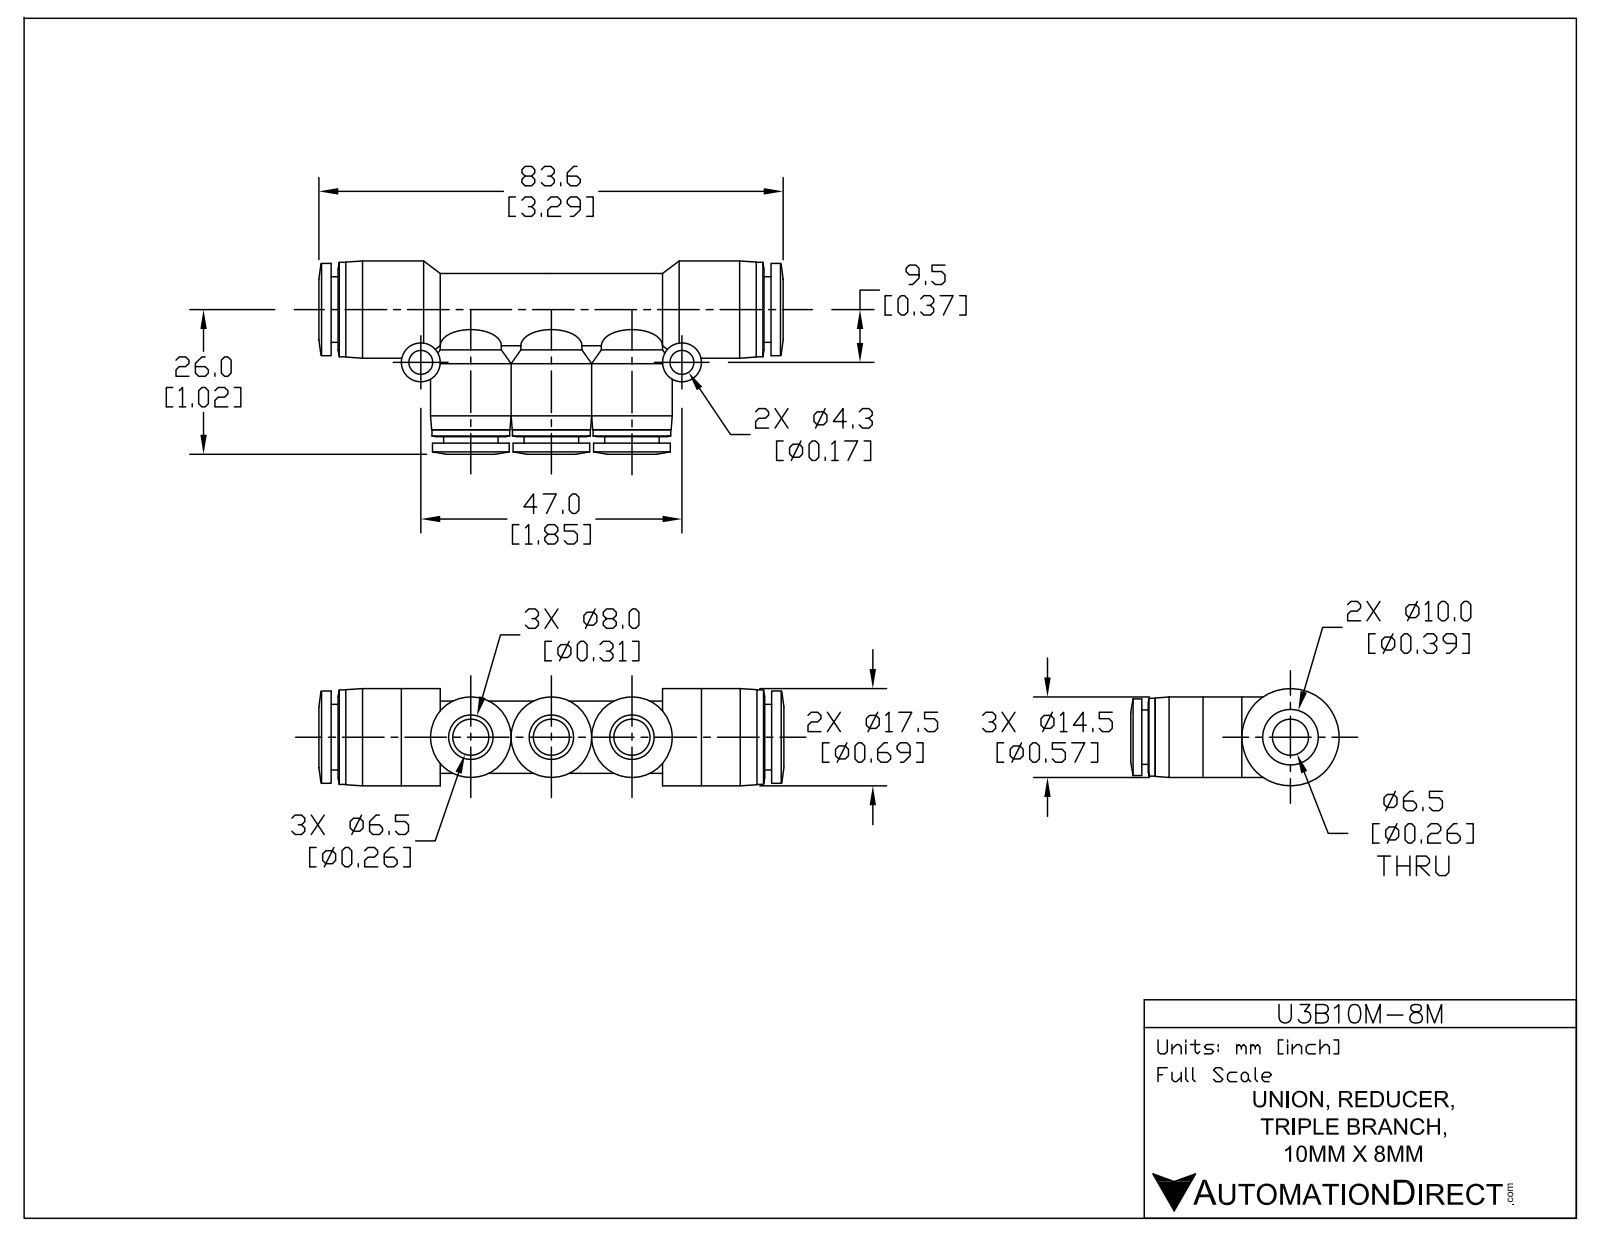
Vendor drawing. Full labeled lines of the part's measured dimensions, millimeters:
Part name (STEP PRODUCT): U3B10M-8M
STEP written by: SolidWorks 2015 (AUTOMOTIVE_DESIGN)
Units: millimetres
Bodies: 1 solid, 153 faces (29 planar, 74 cylindrical, 50 other)
Overall size (bounding box): 83.7 × 34.4 × 17.5
Volume: 15 800 mm³ · Surface area: 12 590 mm²
Round holes (diameter × count): ⌀6.8 ×4, ⌀8.3 ×3, ⌀4.3 ×2, ⌀10.3 ×1
Round bosses / shafts (diameter × count): ⌀14.5 ×3, ⌀14 ×3, ⌀13.8 ×3, ⌀11 ×3, ⌀9.8 ×3, ⌀7 ×2, ⌀17.5 ×1, ⌀17 ×1
Main face-to-face distances: 1.1, 1.2, 78.1, 79.3, 18, 61.3, 16.7, 60, 76.8, 15.1
Hole centre spacings: 14.5, 29, 47
